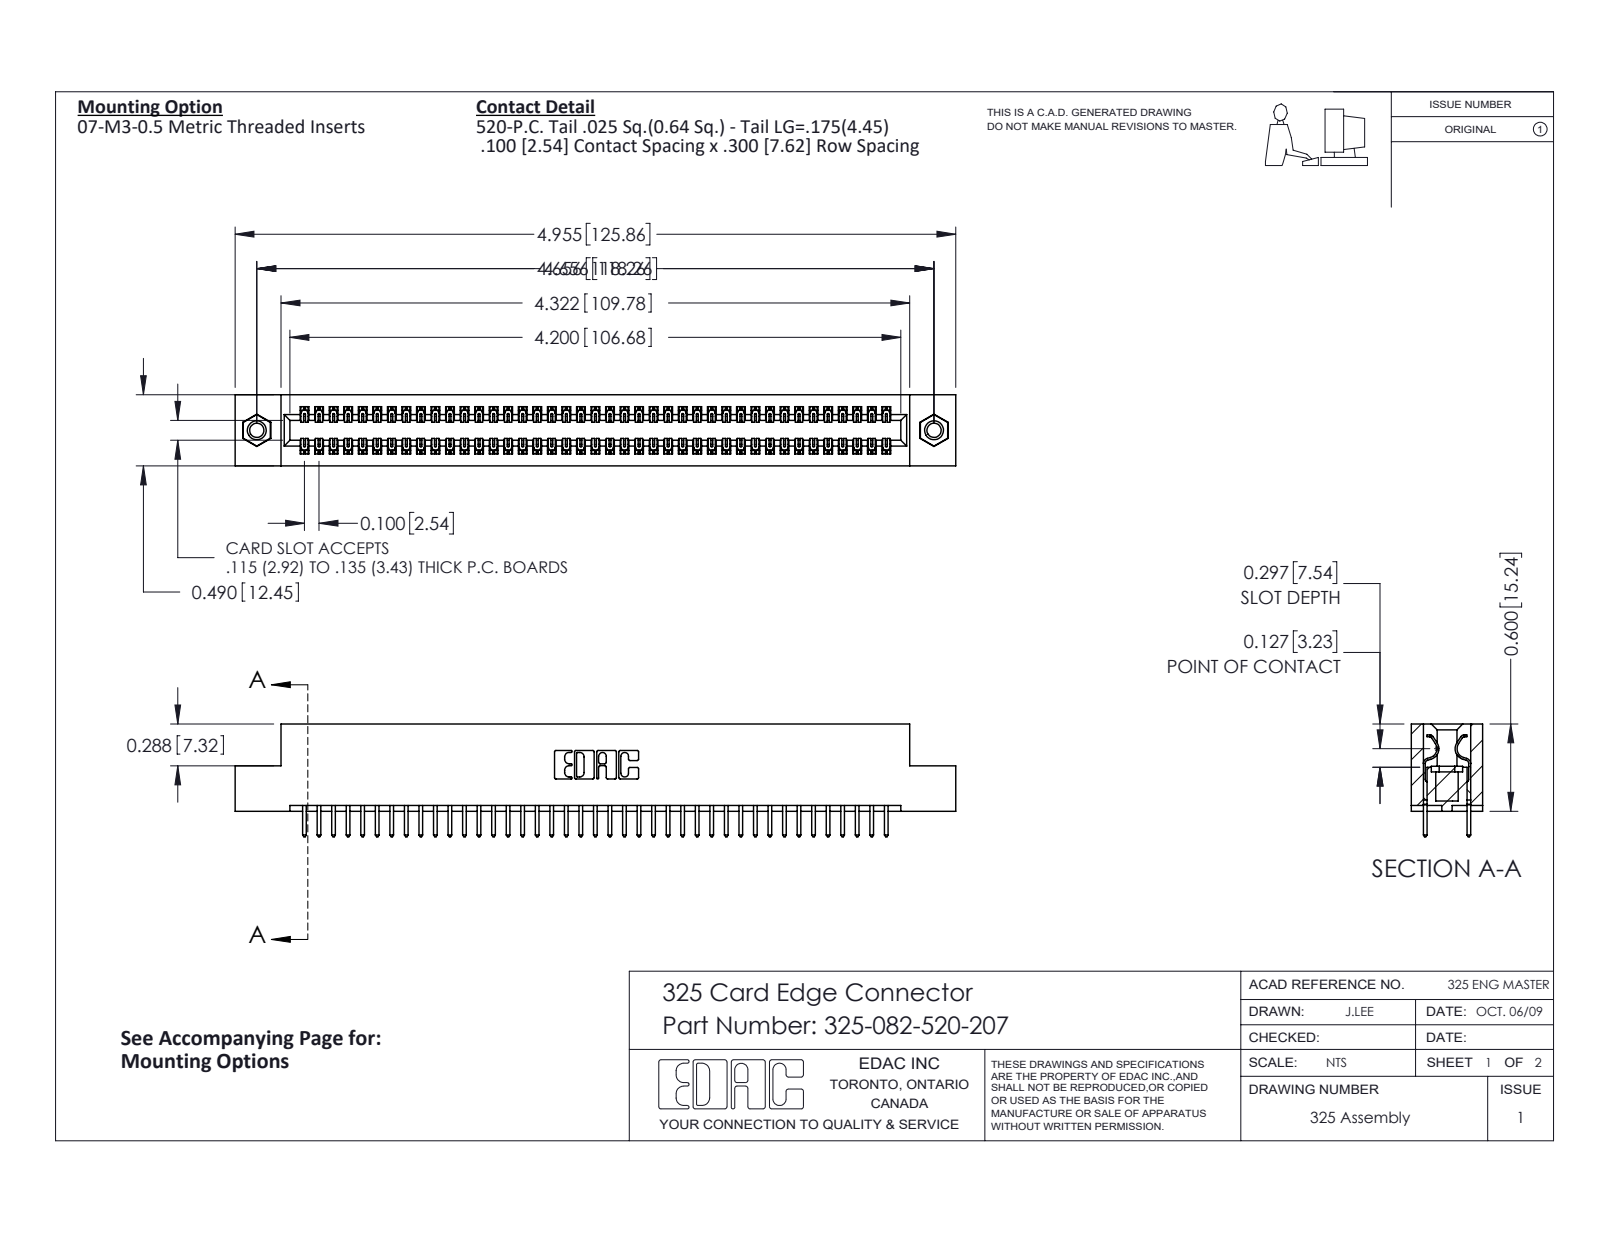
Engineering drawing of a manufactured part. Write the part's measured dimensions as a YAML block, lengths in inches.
part_name: "325-292-001_325-293-120; 325-082-520-207; 345-250-001_345-250-005-103; 325 Part_TI"
step_written_by: "SolidWorks 2016 (CONFIG_CONTROL_DESIGN)"
units: inches
bodies: {solids: 85, faces: 4438, planar: 3054, cylindrical: 1368, other: 16}
overall_size: [4.955, 0.775, 0.49]
volume: 0.989
surface_area: 30.16
round_holes:
  - {diameter: 0.098, count: 2}
  - {diameter: 0.125, count: 2}
  - {diameter: 0.16, count: 2}
round_bosses_or_shafts:
  - {diameter: 0.155, count: 2}
partial_cylinders:
  - {radius: 0.006, count: 123}
  - {radius: 0.01, count: 82}
  - {radius: 0.01, count: 22}
  - {radius: 0.007, count: 6}
  - {radius: 0.031, count: 6}
  - {radius: 0.026, count: 3}
  - {radius: 0.014, count: 2}
  - {radius: 0.022, count: 2}
face_to_face_distances: [0.083, 0.407, 0.3, 0.49, 0.107, 0.383, 0.025, 0.325, 0.275, 0.56]
hole_center_spacings: [4.656]
